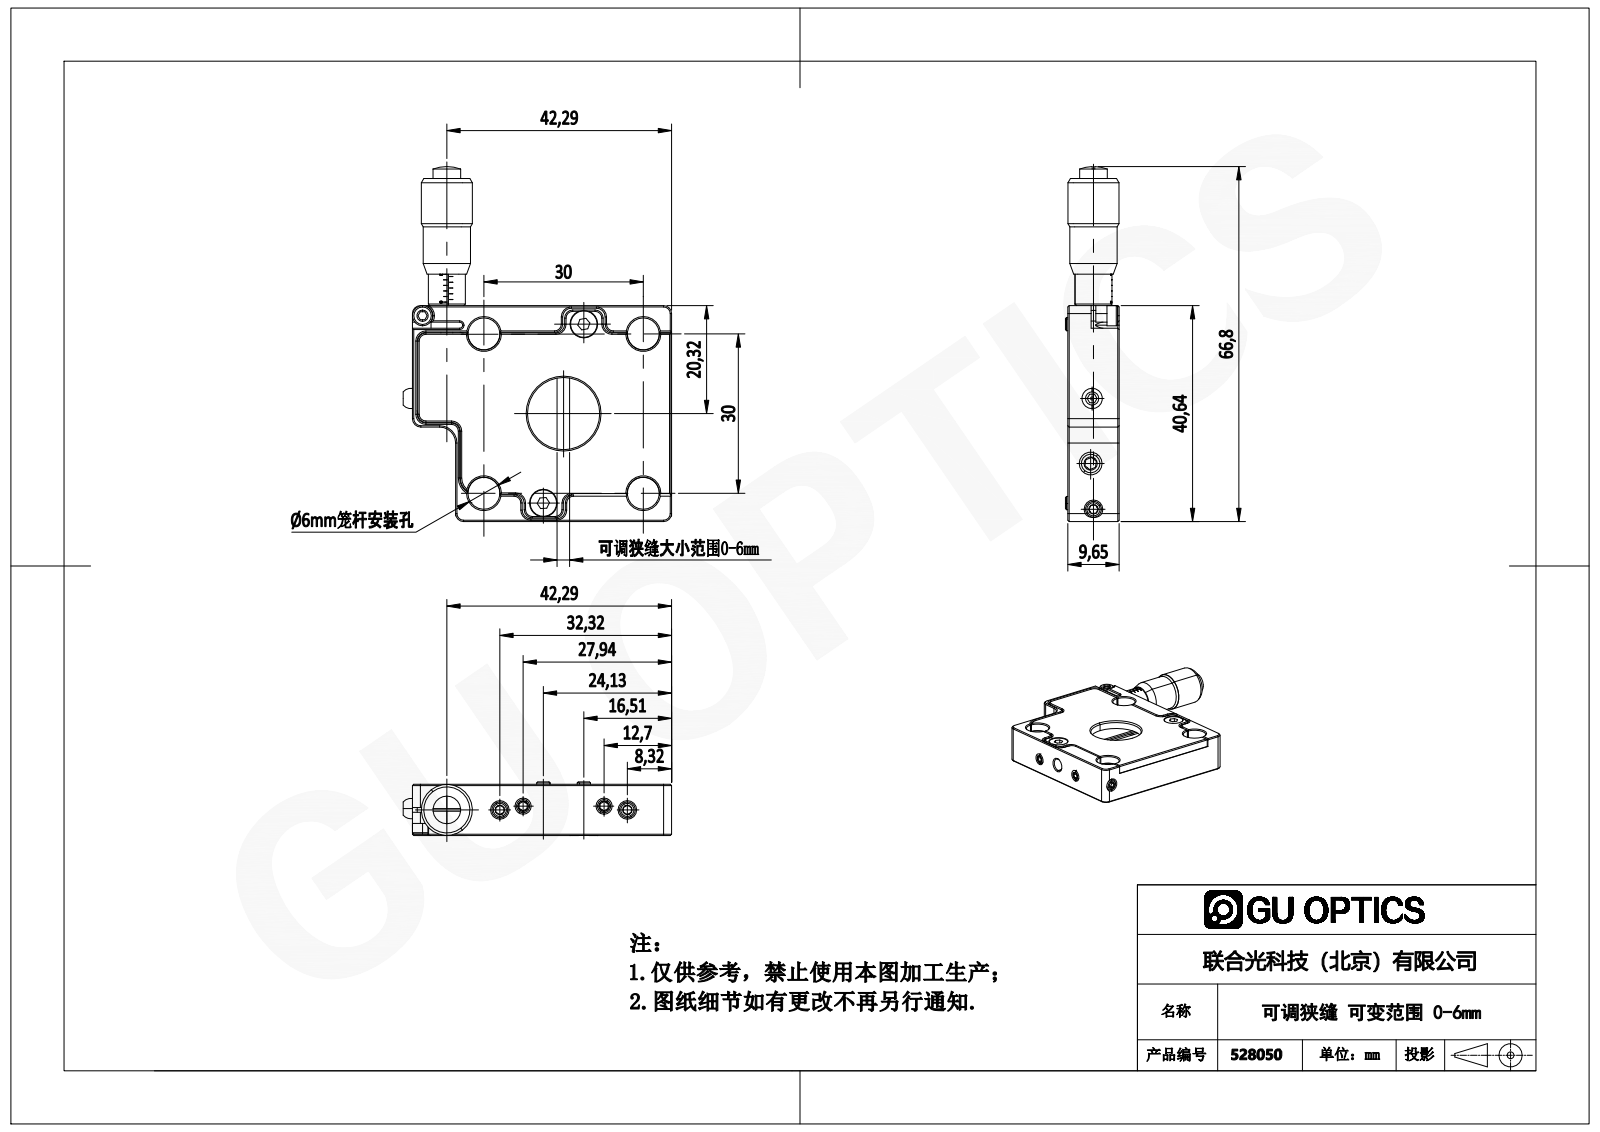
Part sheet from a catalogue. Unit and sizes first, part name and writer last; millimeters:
Units: millimetres
Overall size (bounding box): 66.8 × 50.51 × 10.1
Round holes (diameter × count): ⌀6.02 ×4, ⌀2.5 ×3, ⌀1.6 ×1, ⌀2.39 ×1, ⌀3.3 ×1, ⌀13.59 ×1
Round bosses / shafts (diameter × count): ⌀2.5 ×2, ⌀9.6 ×1, ⌀8.9 ×1, ⌀6.96 ×1, ⌀5.4 ×1, ⌀5.2 ×1, ⌀3.8 ×1, ⌀2 ×1
Partial cylindrical surfaces — rounded edges, fillets, slot ends (radius × count): R1.52 ×12, R1.65 ×10, R3.05 ×5, R1.5 ×4, R1.59 ×4, R1 ×3, R0.13 ×1, R0.57 ×1
Main face-to-face distances: 7.5, 9.66, 2.16, 7.62, 2.04, 5.46, 6.2, 4.16, 1.3, 3.46
Hole centre spacings: 21.21, 30, 12, 42.43, 12.04, 24, 32.31, 35.36
Bodies: 0 solids, 553 faces (253 planar, 115 cylindrical, 185 other)
Part name (STEP PRODUCT): 2.2.6.2，L30G-KX，30mm笼式系统可变狭隙，A
STEP written by: SolidWorks 2018 (AUTOMOTIVE_DESIGN)
